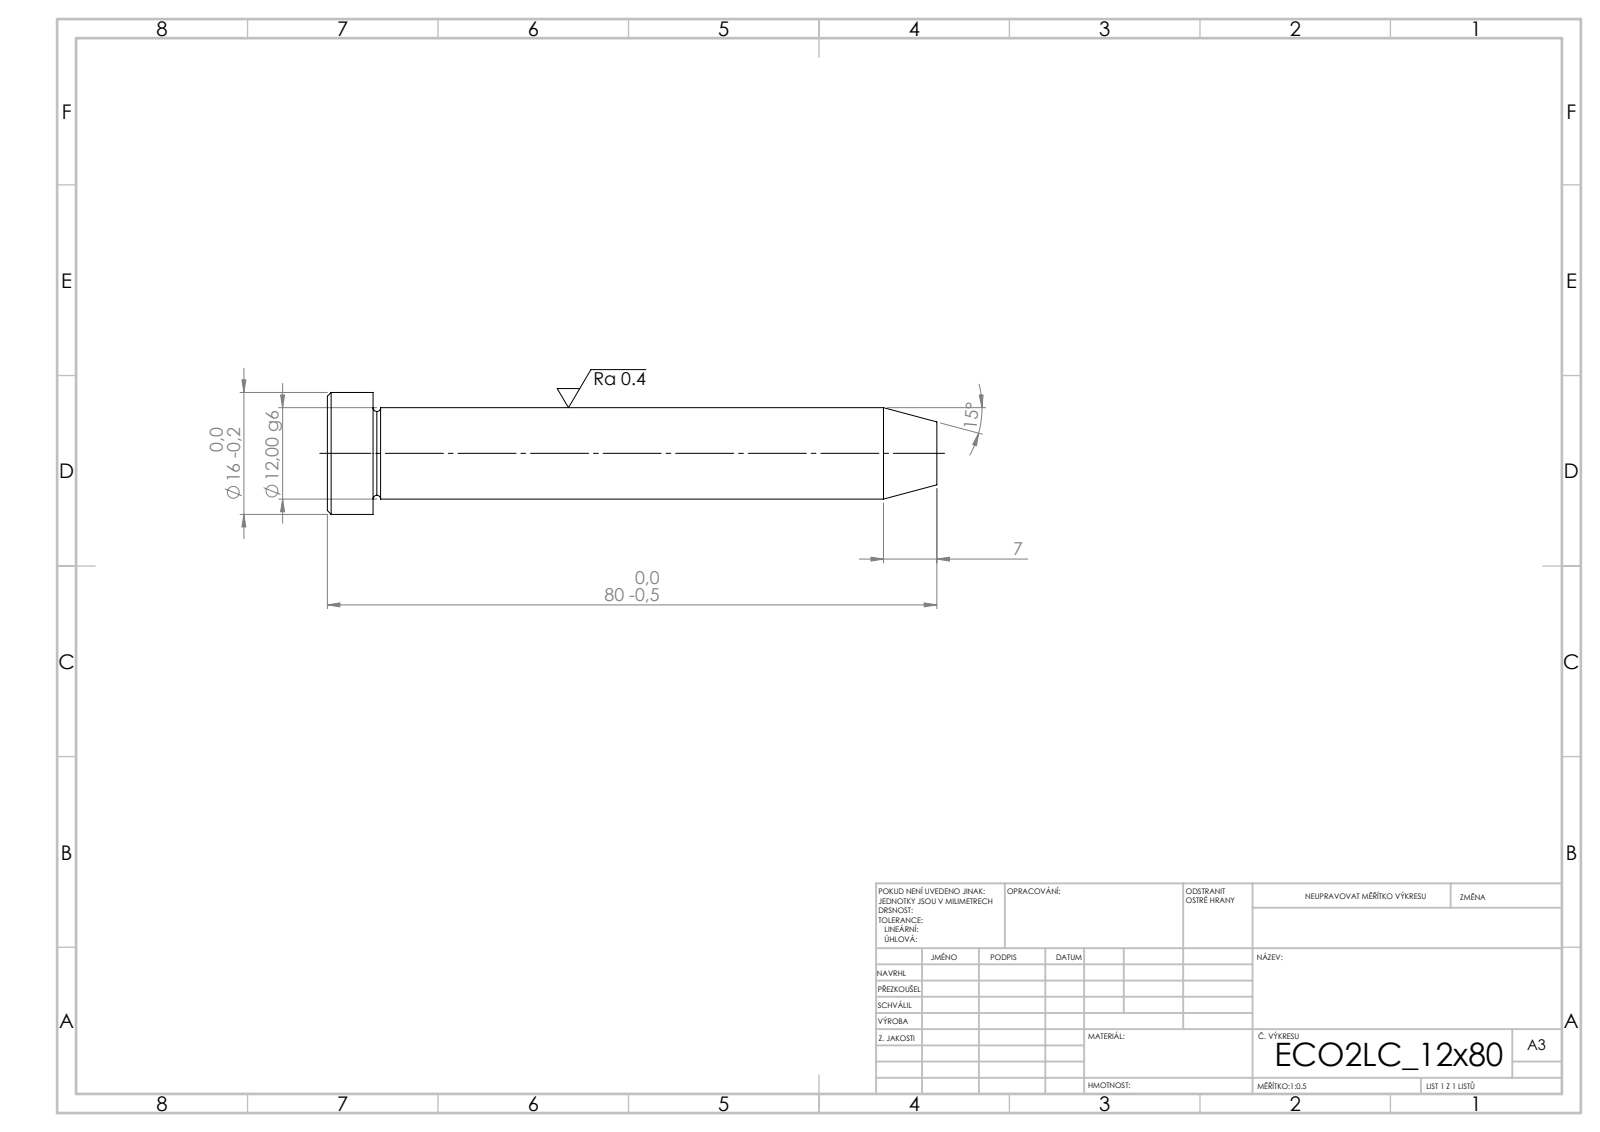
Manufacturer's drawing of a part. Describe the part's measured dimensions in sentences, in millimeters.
Its 3-D file was written by "SolidWorks 2019 (CONFIG_CONTROL_DESIGN)". It is 1 solid with 15 faces: 3 planar, 4 cylindrical and 8 other. Overall it measures 80 by 16 by 16 millimeters. Its volume is 9 333 cubic millimeters and its surface area 3 404 square millimeters. Round bosses or shafts: 1 of diameter 16, 1 of diameter 12. The main face-to-face distances are 6, 74, 80.
